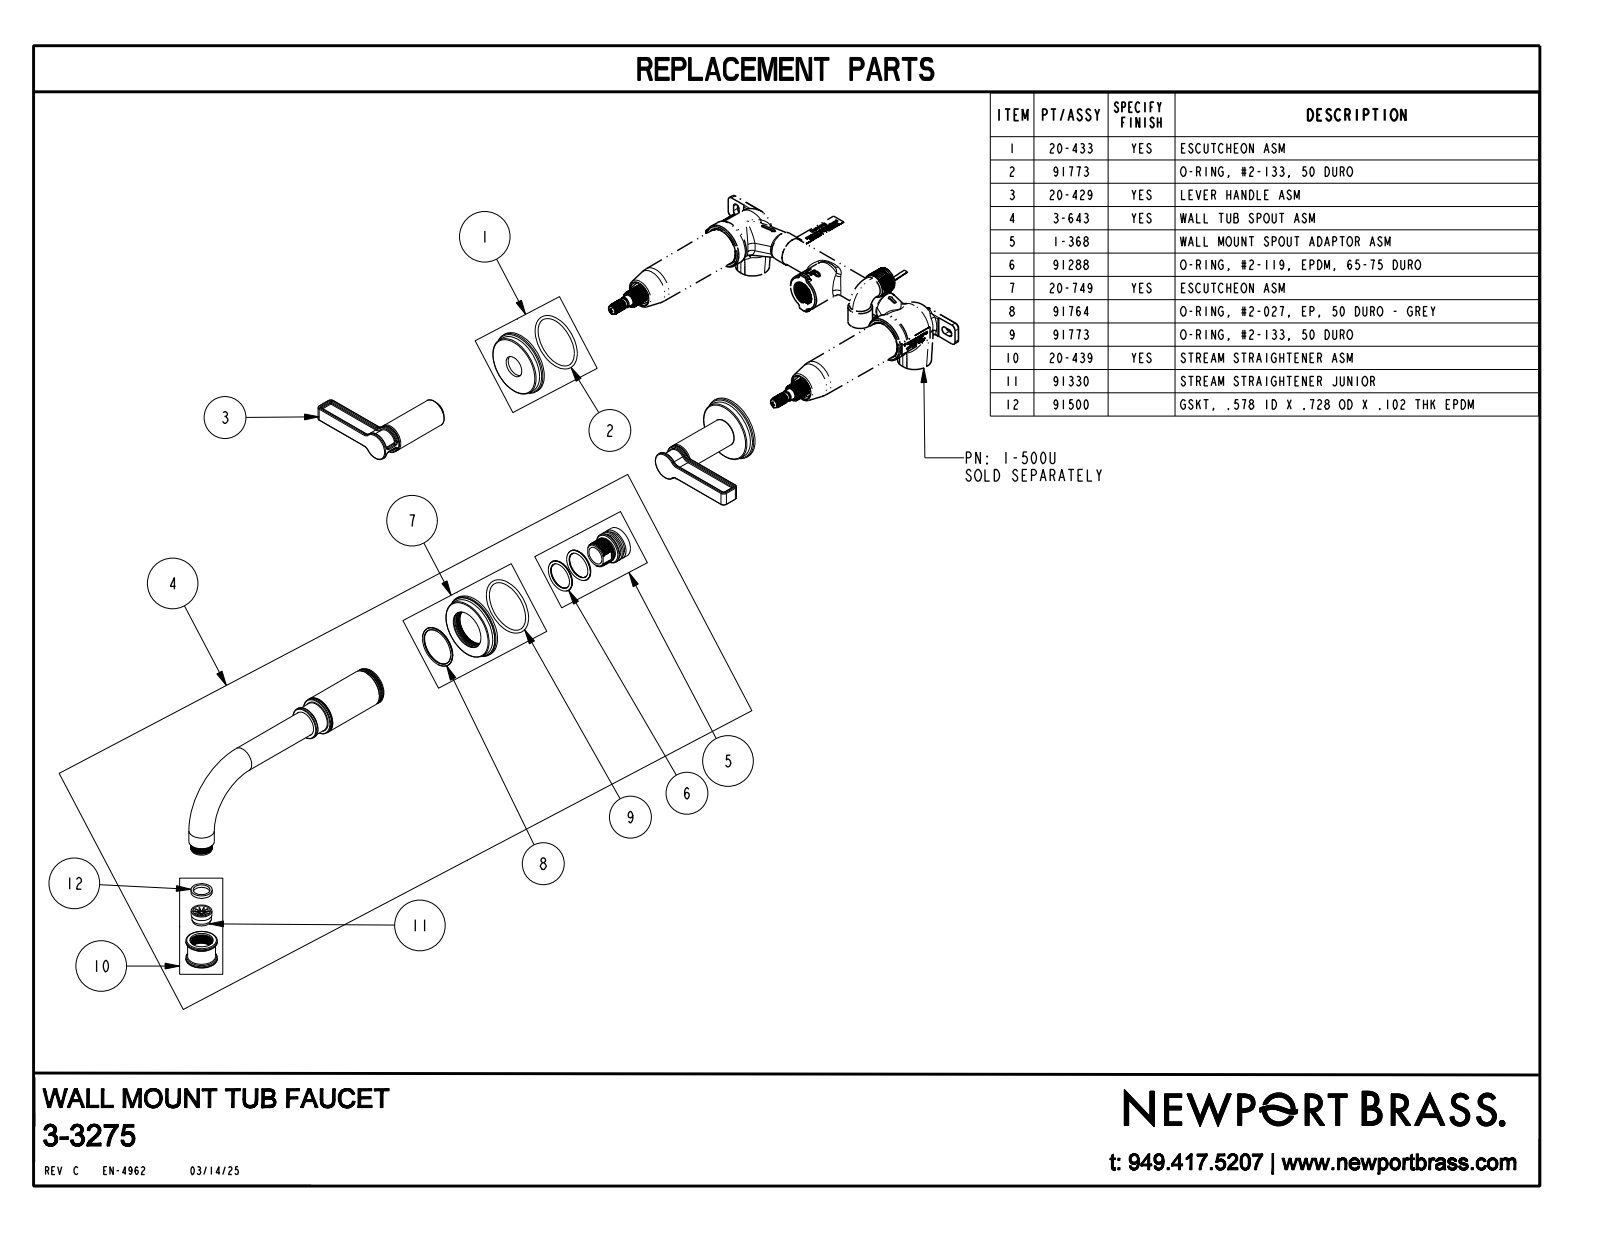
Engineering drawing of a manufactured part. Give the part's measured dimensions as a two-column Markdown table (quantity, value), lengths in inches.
| quantity | value |
| --- | --- |
| part name | 3-3275_SW0001 |
| STEP written by | CREO PARAMETRIC BY PTC INC, 2018400 (AUTOMOTIVE_DESIGN) |
| units | inches |
| bodies | 3 solids, 316 faces (46 planar, 126 cylindrical, 144 other) |
| overall size | 13.575 × 10.385 × 8.79 |
| volume | 17.28 in³ |
| surface area | 96.64 in² |
| round bosses / shafts (diameter × count) | 2.25 × 3, 2.09 × 3, 0.975 × 2, 0.875 × 2, 0.85 × 2, 0.5 × 2, 1.312 × 1, 1.14 × 1 |
| partial cylindrical surfaces (radius × count) | 0.025 × 32, 0.03 × 4, 0.1 × 4, 0.13 × 4, 0.25 × 4, 0.35 × 4, 0.387 × 2 |
| main face-to-face distances | 0.35, 3.251, 2.901, 2.551, 2.201, 0.7, 0.1, 0.3, 0.6, 0.5 |
